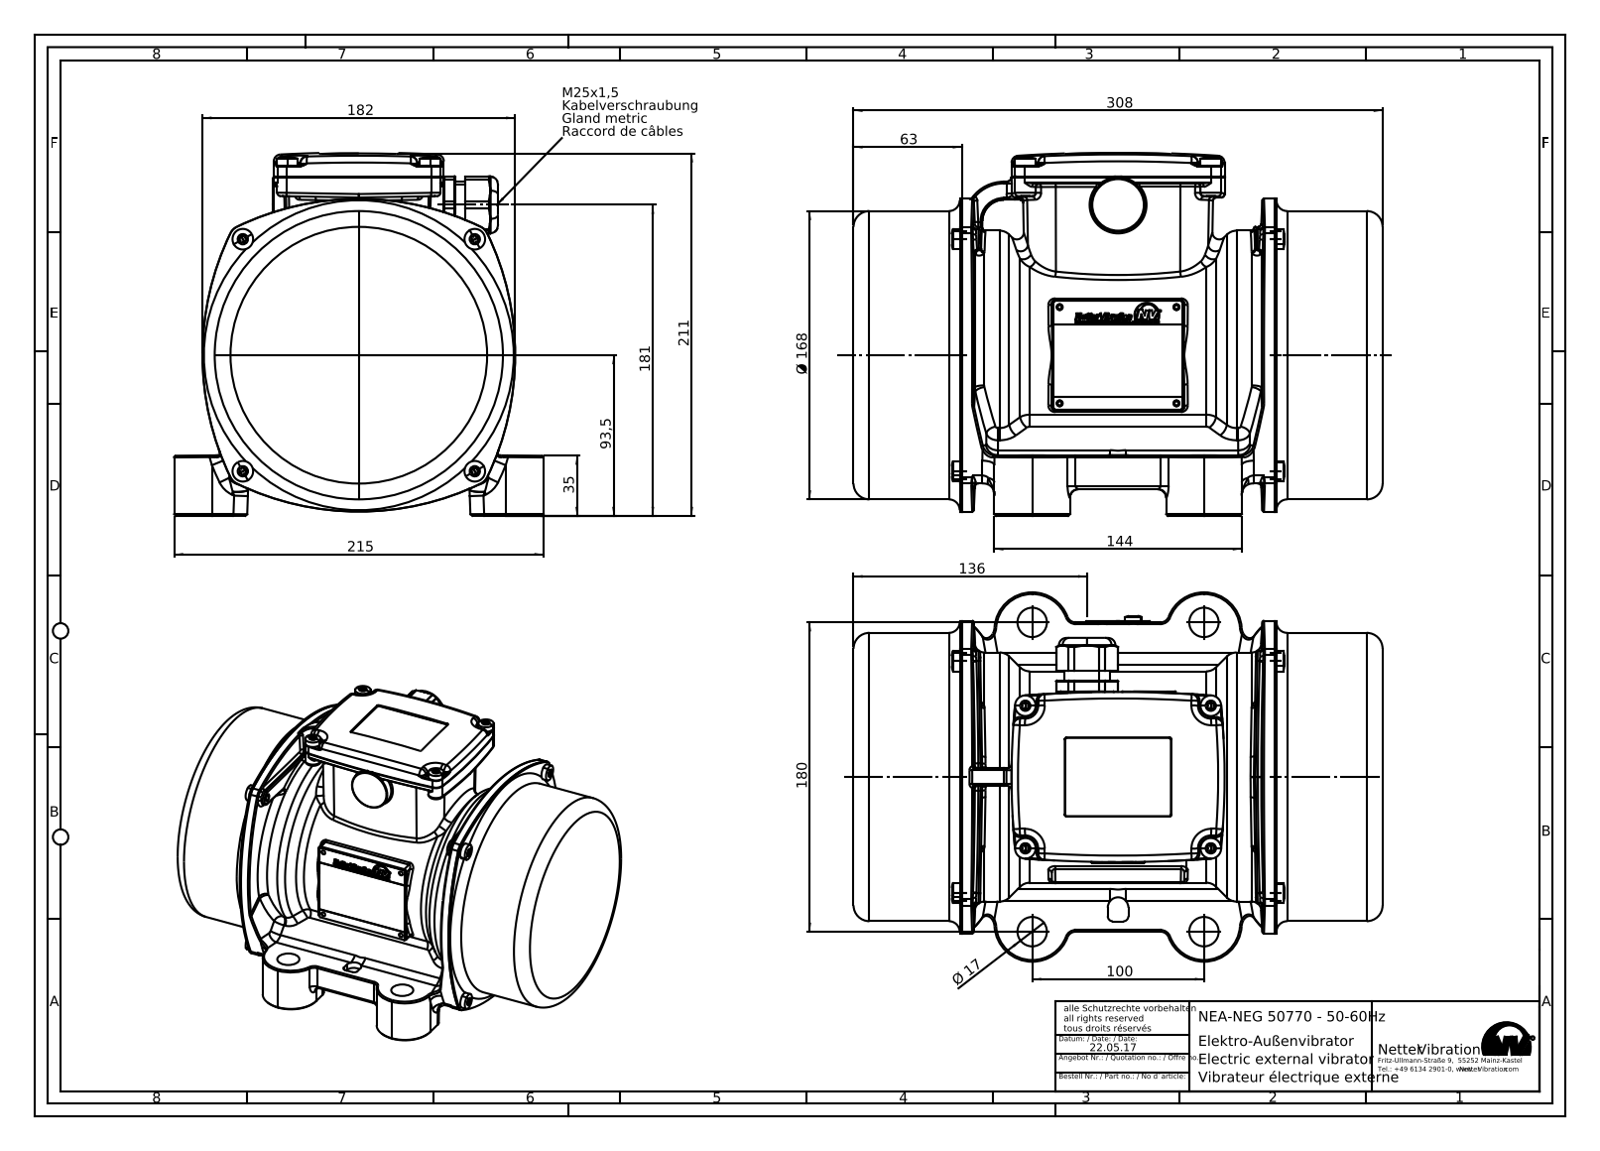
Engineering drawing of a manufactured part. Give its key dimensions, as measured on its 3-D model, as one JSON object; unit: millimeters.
{"part_name": "NEA-NEG 50770-50-60Hz", "step_written_by": "SolidWorks 2015 (AUTOMOTIVE_DESIGN)", "units": "millimeters", "bodies": {"solids": 23, "faces": 2952, "planar": 927, "cylindrical": 635, "other": 1390}, "overall_size": [308, 215, 211.21], "volume_mm3": 1543000, "surface_area_mm2": 632060, "round_holes": [[3.4, 4], [4.5, 4], [6.5, 4], [9, 4], [16, 2], [11, 1], [18.5, 1], [23.5, 1], [110.4, 1], [130, 1], [165.4, 1], [176.5, 1]], "round_bosses_or_shafts": [[12, 8], [6, 8], [10, 2], [5, 2], [167.8, 1], [165, 1], [164.8, 1], [145, 1]], "partial_cylinders_radius": [[1, 30], [0.5, 28], [2, 26], [0.3, 20], [5, 20], [10, 16], [3, 14], [8, 14]], "face_to_face_distances": [1.2, 306.8, 245, 61.8, 305.6, 308, 9, 54, 254, 52.8], "hole_center_spacings": [95.5, 135.06, 47.59, 56, 59.07, 68, 83, 88.09]}
